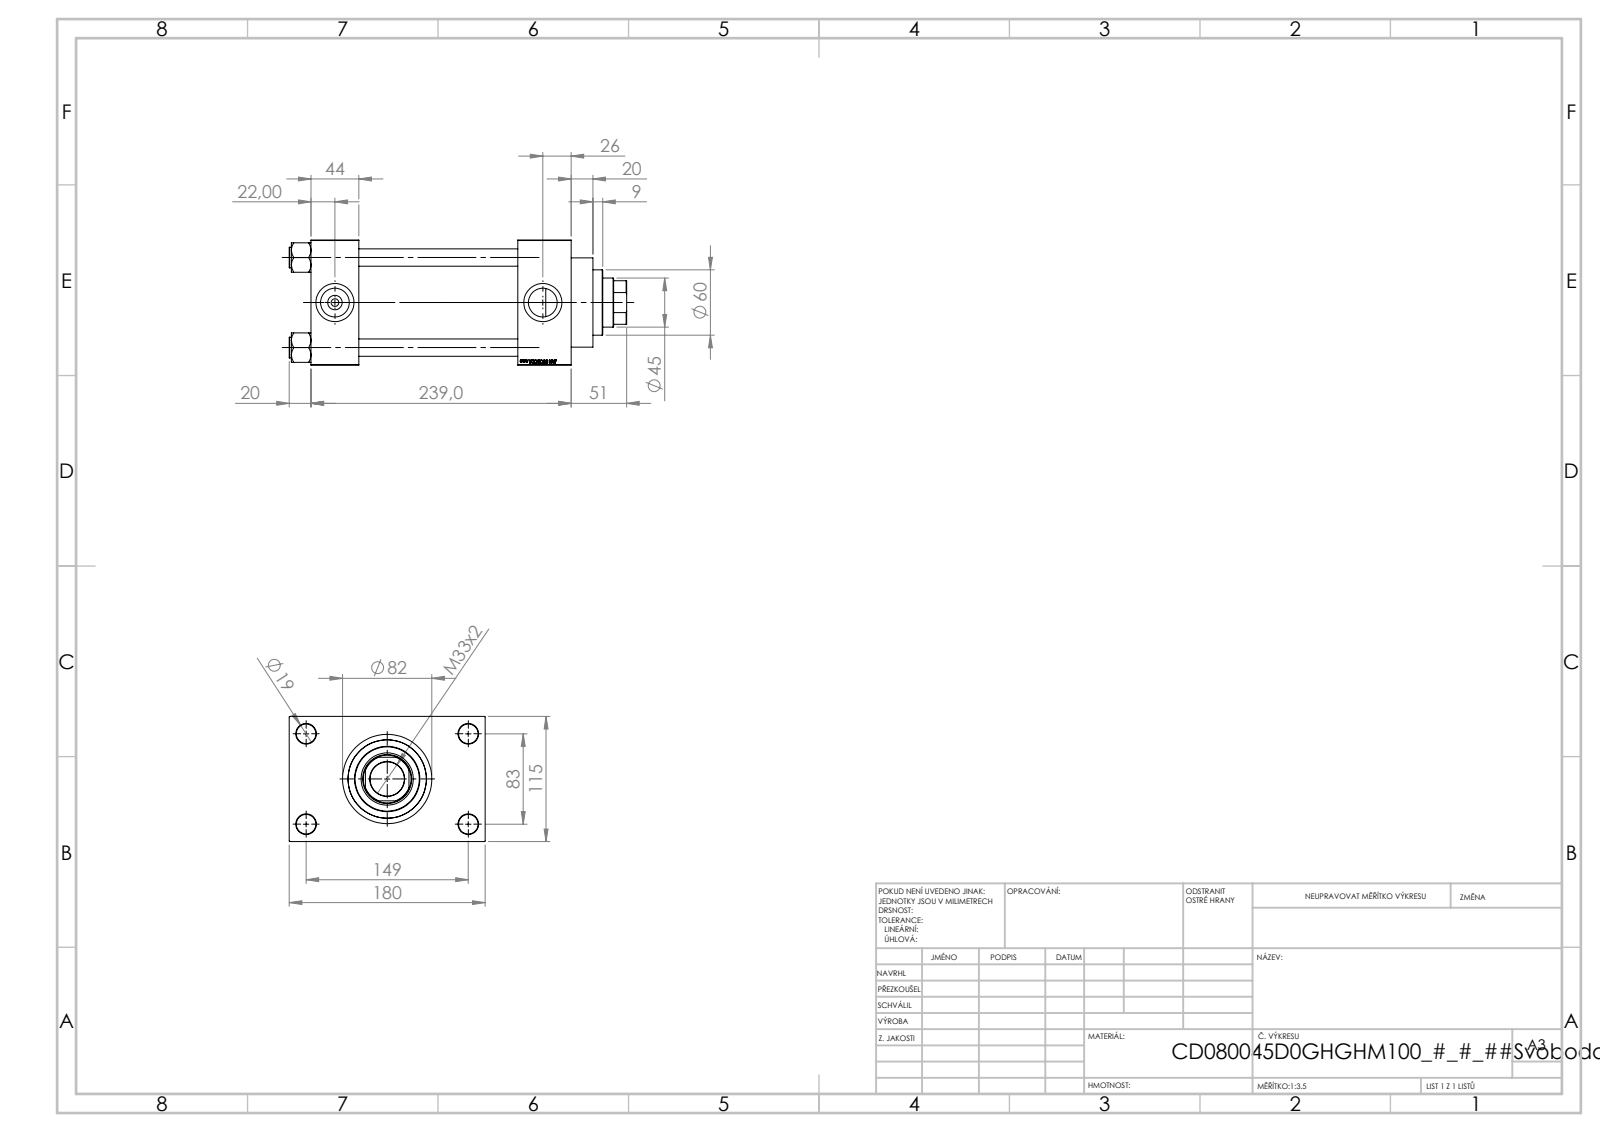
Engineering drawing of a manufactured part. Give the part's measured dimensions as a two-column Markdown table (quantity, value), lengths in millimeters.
| quantity | value |
| --- | --- |
| part name | V215CD_NUT_M5_D; V215CD_VCP_D; V215CD_D_TYCINKA; V215CD_D_Body (+1 more) |
| STEP written by | SolidWorks 2019 (CONFIG_CONTROL_DESIGN) |
| units | millimeters |
| bodies | 11 solids, 1151 faces (545 planar, 88 cylindrical, 518 other) |
| overall size | 310 × 180 × 115 |
| volume | 2 258 000 mm³ |
| surface area | 371 564 mm² |
| round holes (diameter × count) | 16 × 4, 18 × 4, 7 × 2, 26.44 × 2, 35 × 2, 31.5 × 1, 45 × 1, 48 × 1, 61 × 1, 72 × 1, 80 × 1 |
| round bosses / shafts (diameter × count) | 19 × 4, 86 × 1, 82 × 1, 60 × 1 |
| partial cylindrical surfaces (radius × count) | 22 × 1 |
| main face-to-face distances | 115, 146, 195, 49, 44, 190, 239, 32.5, 147.5, 180 |
| hole center spacings | 33.15, 58.48, 82.7, 85.28, 89.24, 115.85, 142.43, 83 |
